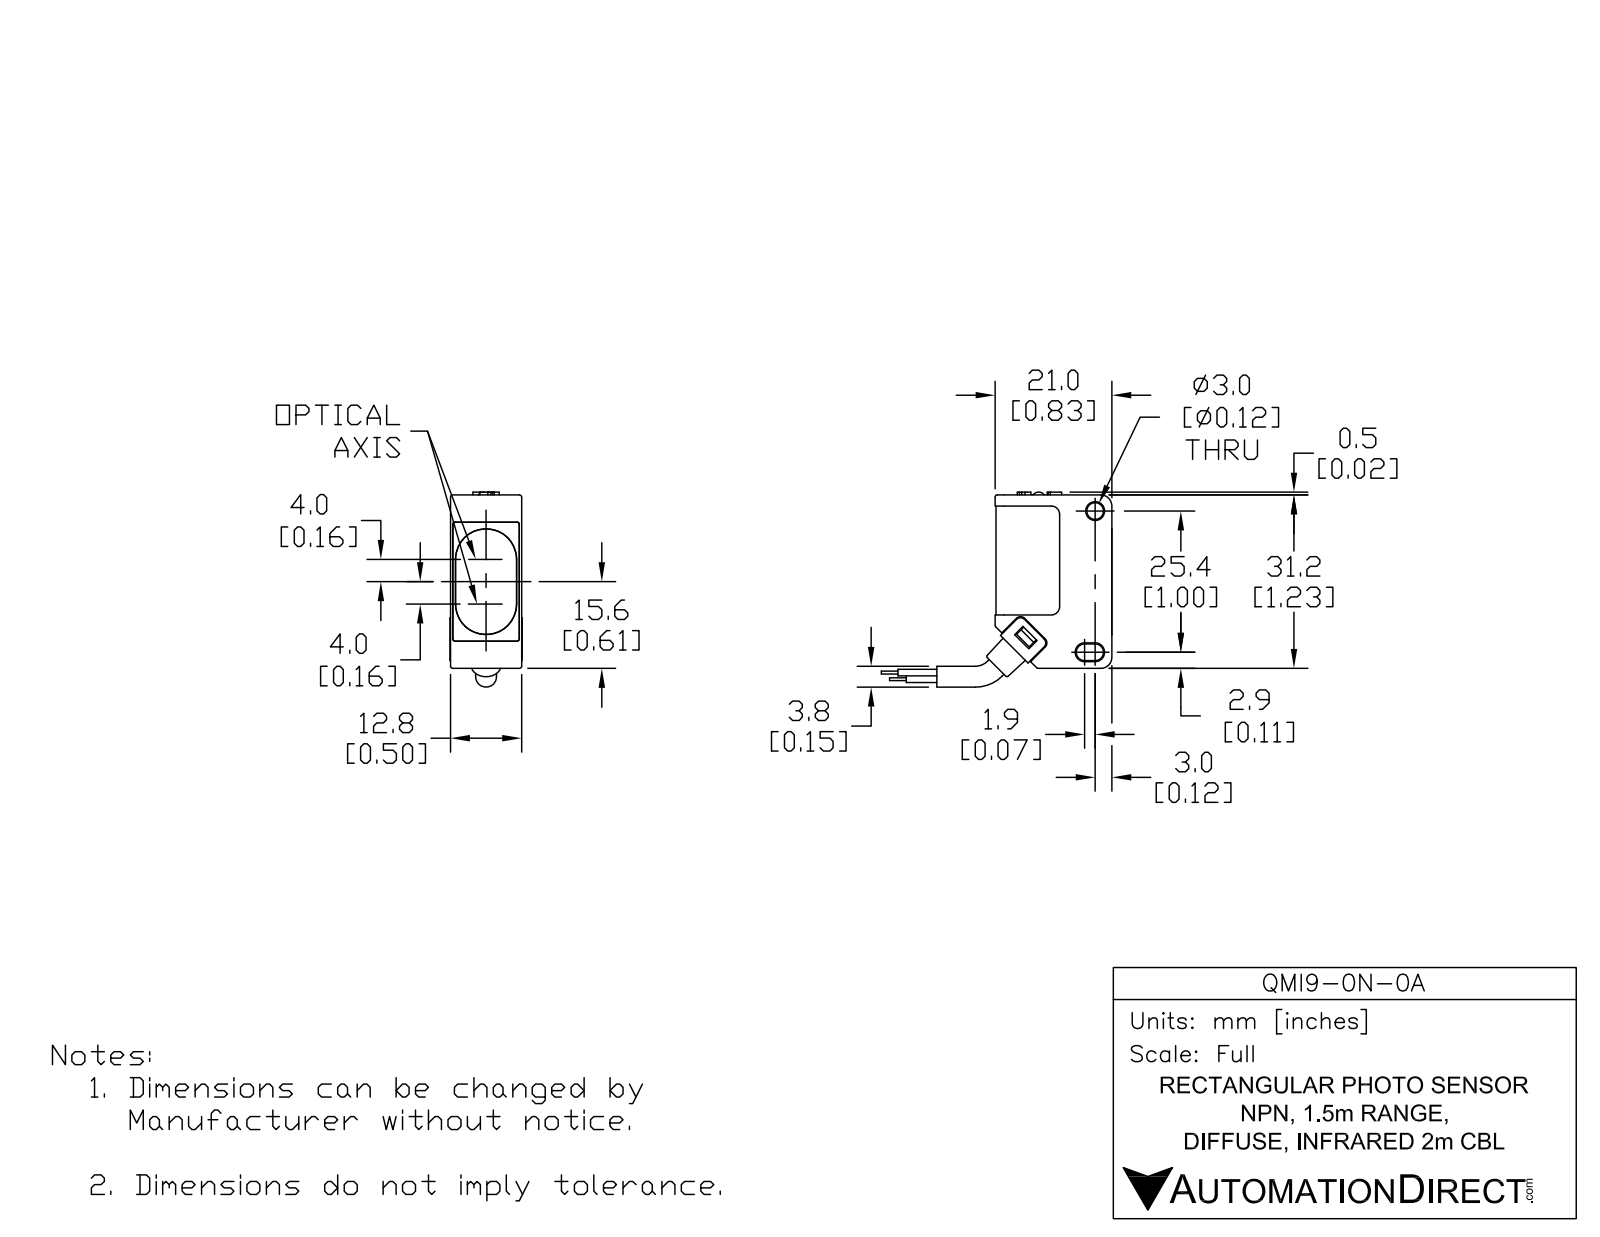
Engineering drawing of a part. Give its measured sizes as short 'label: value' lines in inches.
name: QMI9-0N-0A
written by: SolidWorks 2017 (AUTOMOTIVE_DESIGN)
unit: in
bodies: 9 solids, 258 faces (134 planar, 100 cylindrical, 24 other)
size: 3.193 × 1.032 × 0.512
volume: 0.47 in³; area: 8.375 in²
holes: 3× ⌀0.118, 1× ⌀0.148, 1× ⌀0.224, 1× ⌀0.283
bosses: 2× ⌀0.138
rounds: 13× R0.016, 10× R0.02, 8× R0.039, 6× R0.059, 4× R0.024, 2× R0.006, 2× R0.035, 2× R0.044
face distances: 0.02, 0.498, 0.059, 0.016, 0.504, 0.138, 0.488, 0.079, 0.482, 0.492
hole spacings: 0.205
